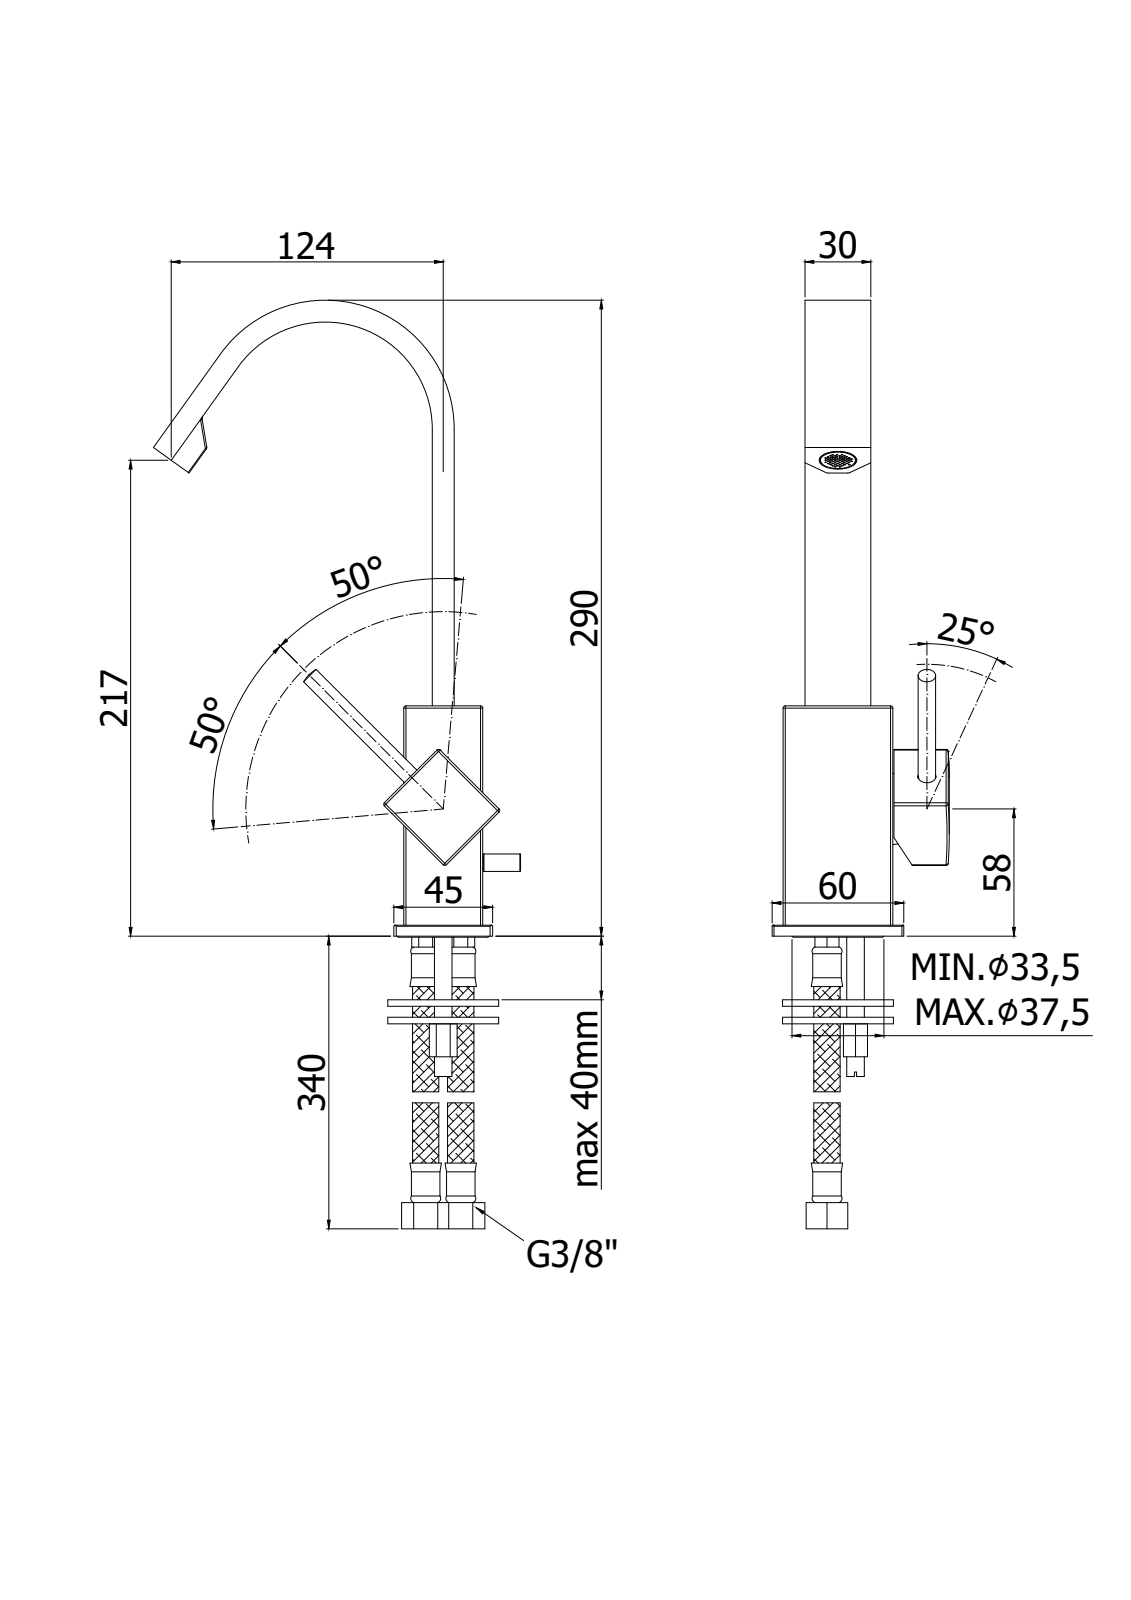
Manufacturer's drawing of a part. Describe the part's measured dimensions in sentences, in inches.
The part is named "LEA878CR". Its 3-D file was written by "CREO PARAMETRIC BY PTC INC, 2020044 (CONFIG_CONTROL_DESIGN)". It is 2 solids with 3106 faces: 1971 planar, 665 cylindrical and 470 other. Overall it measures 11.417 by 6.23 by 3.267 inches. Its volume is 14.27 cubic inches and its surface area 164.7 square inches. Round holes: 4 of diameter 0.433, 3 of diameter 0.197, 3 of diameter 0.236, 2 of diameter 0.13, 2 of diameter 0.177, 2 of diameter 0.276, 2 of diameter 0.354, 2 of diameter 1.339, 1 of diameter 0.118, 1 of diameter 0.157, 1 of diameter 0.217, 1 of diameter 0.268. Round bosses or shafts: 3 of diameter 0.035, 2 of diameter 0.787, 1 of diameter 1.528, 1 of diameter 1.26, 1 of diameter 1.24, 1 of diameter 0.984, 1 of diameter 0.937, 1 of diameter 0.89. Partial cylindrical surfaces (rounded edges, fillets, slot ends): 64 of radius 0.02, 51 of radius 0.005, 19 of radius 0.039, 10 of radius 0.028, 9 of radius 0.024, 6 of radius 0.031, 4 of radius 0.026, 4 of radius 0.033. The main face-to-face distances are 0.059, 0.394, 0.335, 0.512, 0.906, 0.846, 1.575, 0.571, 1.417, 0.453. The hole center spacings are 0.235, 0.265, 0.371, 0.398, 0.441, 0.445, 0.601, 0.711.
